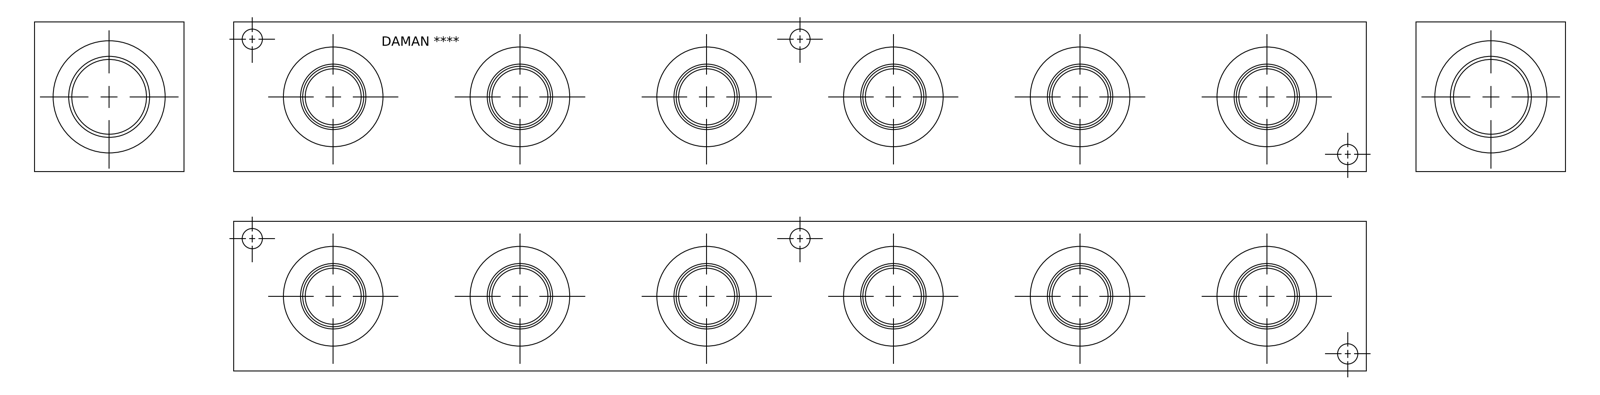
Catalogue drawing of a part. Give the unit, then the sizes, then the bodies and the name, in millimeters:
Units: millimetres
Overall size (bounding box): 577.85 × 76.2 × 76.2
Round holes (diameter × count): ⌀31.27 ×12, ⌀33.76 ×12, ⌀49.12 ×12, ⌀33.35 ×11, ⌀35.51 ×11, ⌀28.57 ×8, ⌀10.31 ×6, ⌀33.34 ×1, ⌀38.1 ×1, ⌀39.22 ×1, ⌀41.27 ×1, ⌀41.28 ×1
Partial cylindrical surfaces — rounded edges, fillets, slot ends (radius × count): R14.29 ×4
Main face-to-face distances: 76.2, 0.79, 75.41, 577.85, 577.06, 19.84, 19.05, 56.36, 576.27, 558.01
Hole centre spacings: 95.25, 190.5, 285.75, 381, 50.65, 50.66, 55.94, 55.95
Volume: 2 877 000 mm³ · Surface area: 243 348 mm²
Bodies: 1 solid, 551 faces (235 planar, 97 cylindrical, 219 other)
Part name (STEP PRODUCT): Part_+H0900616S_3D
STEP written by: Autodesk Inventor 2020 (AUTOMOTIVE_DESIGN)
